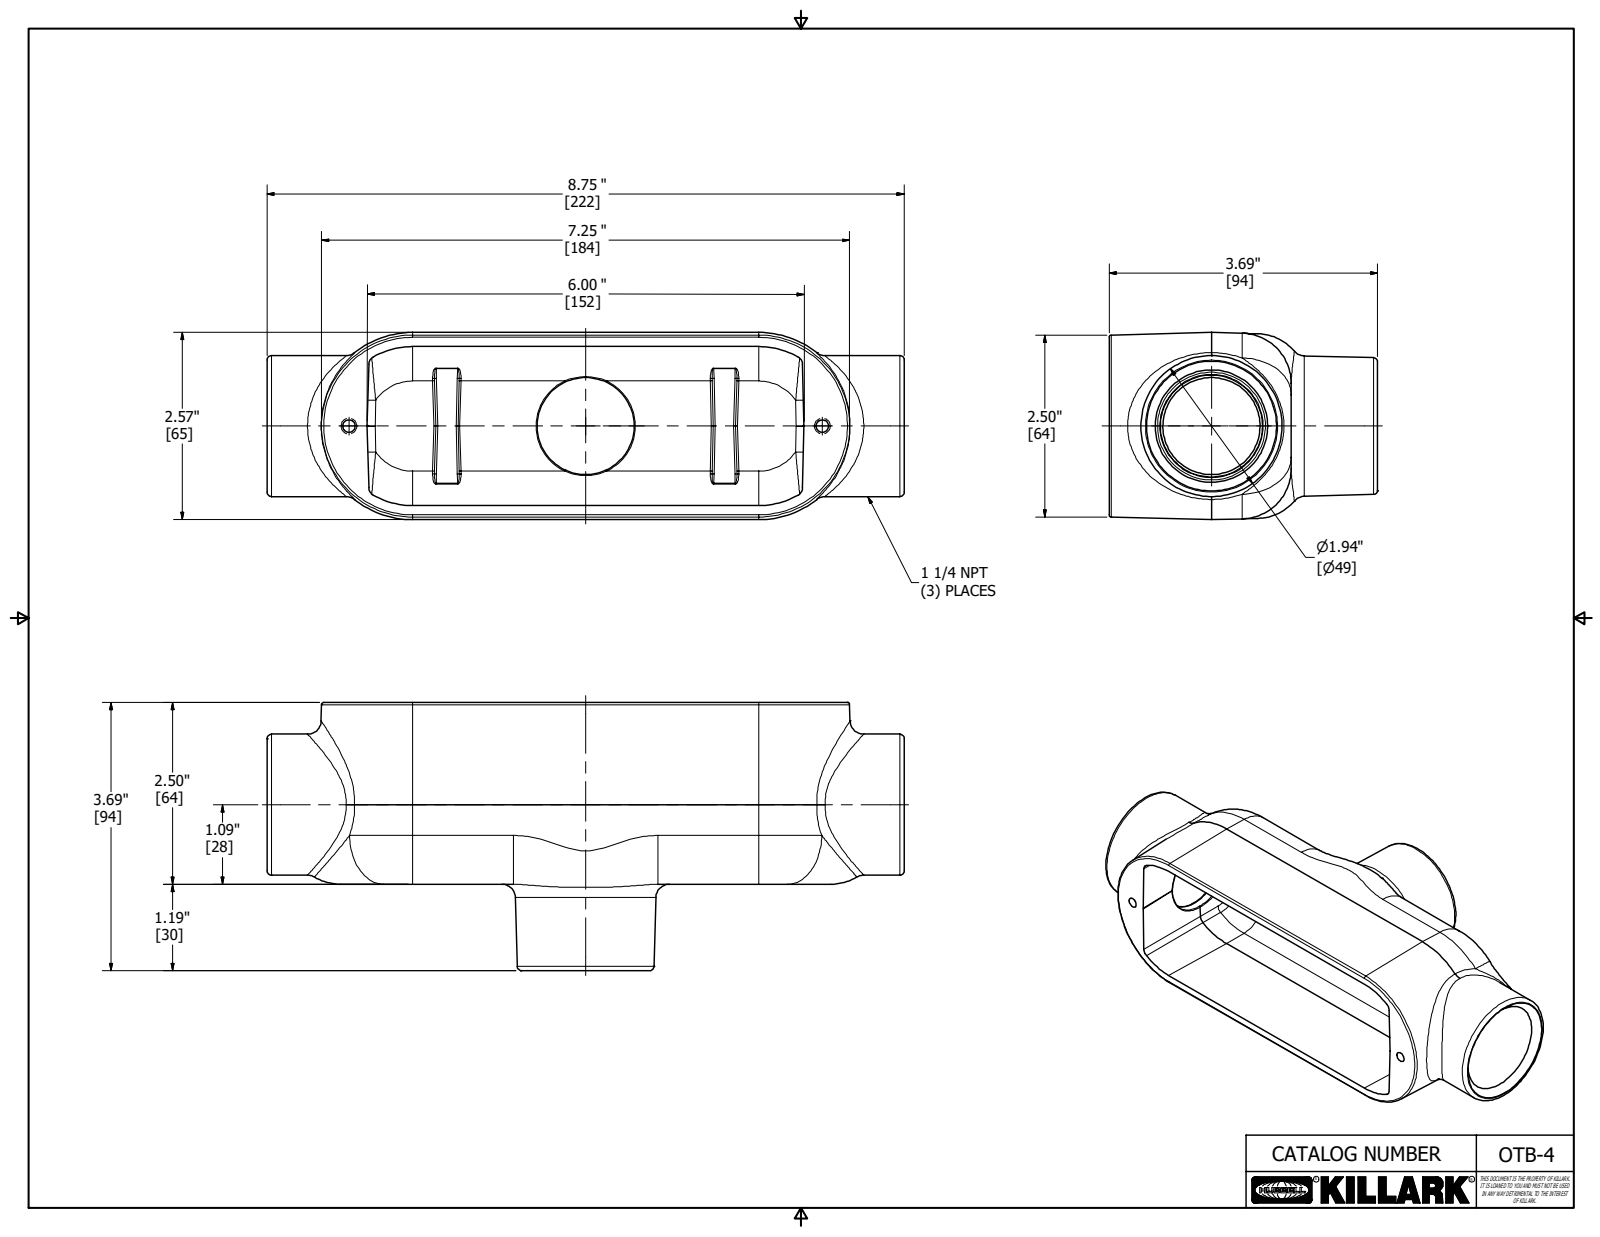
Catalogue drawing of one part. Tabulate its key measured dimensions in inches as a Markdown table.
| quantity | value |
| --- | --- |
| part name | 13931-1 |
| STEP written by | Autodesk Inventor 2018 (AUTOMOTIVE_DESIGN) |
| units | inches |
| bodies | 1 solid, 385 faces (154 planar, 67 cylindrical, 164 other) |
| overall size | 8.75 × 3.688 × 2.574 |
| volume | 12.6 in³ |
| surface area | 133.6 in² |
| round holes (diameter × count) | 0.171 × 2, 1.334 × 2 |
| round bosses / shafts (diameter × count) | 1.938 × 1 |
| partial cylindrical surfaces (radius × count) | 0.03 × 18, 0.031 × 14, 0.125 × 4, 0.25 × 4, 0.5 × 2, 0.687 × 2 |
| main face-to-face distances | 0.156, 2.417, 2.573, 0.156, 2.261, 2.417, 0.187, 2.5, 2.313, 0.031 |
| hole center spacings | 3.25, 6.5 |
